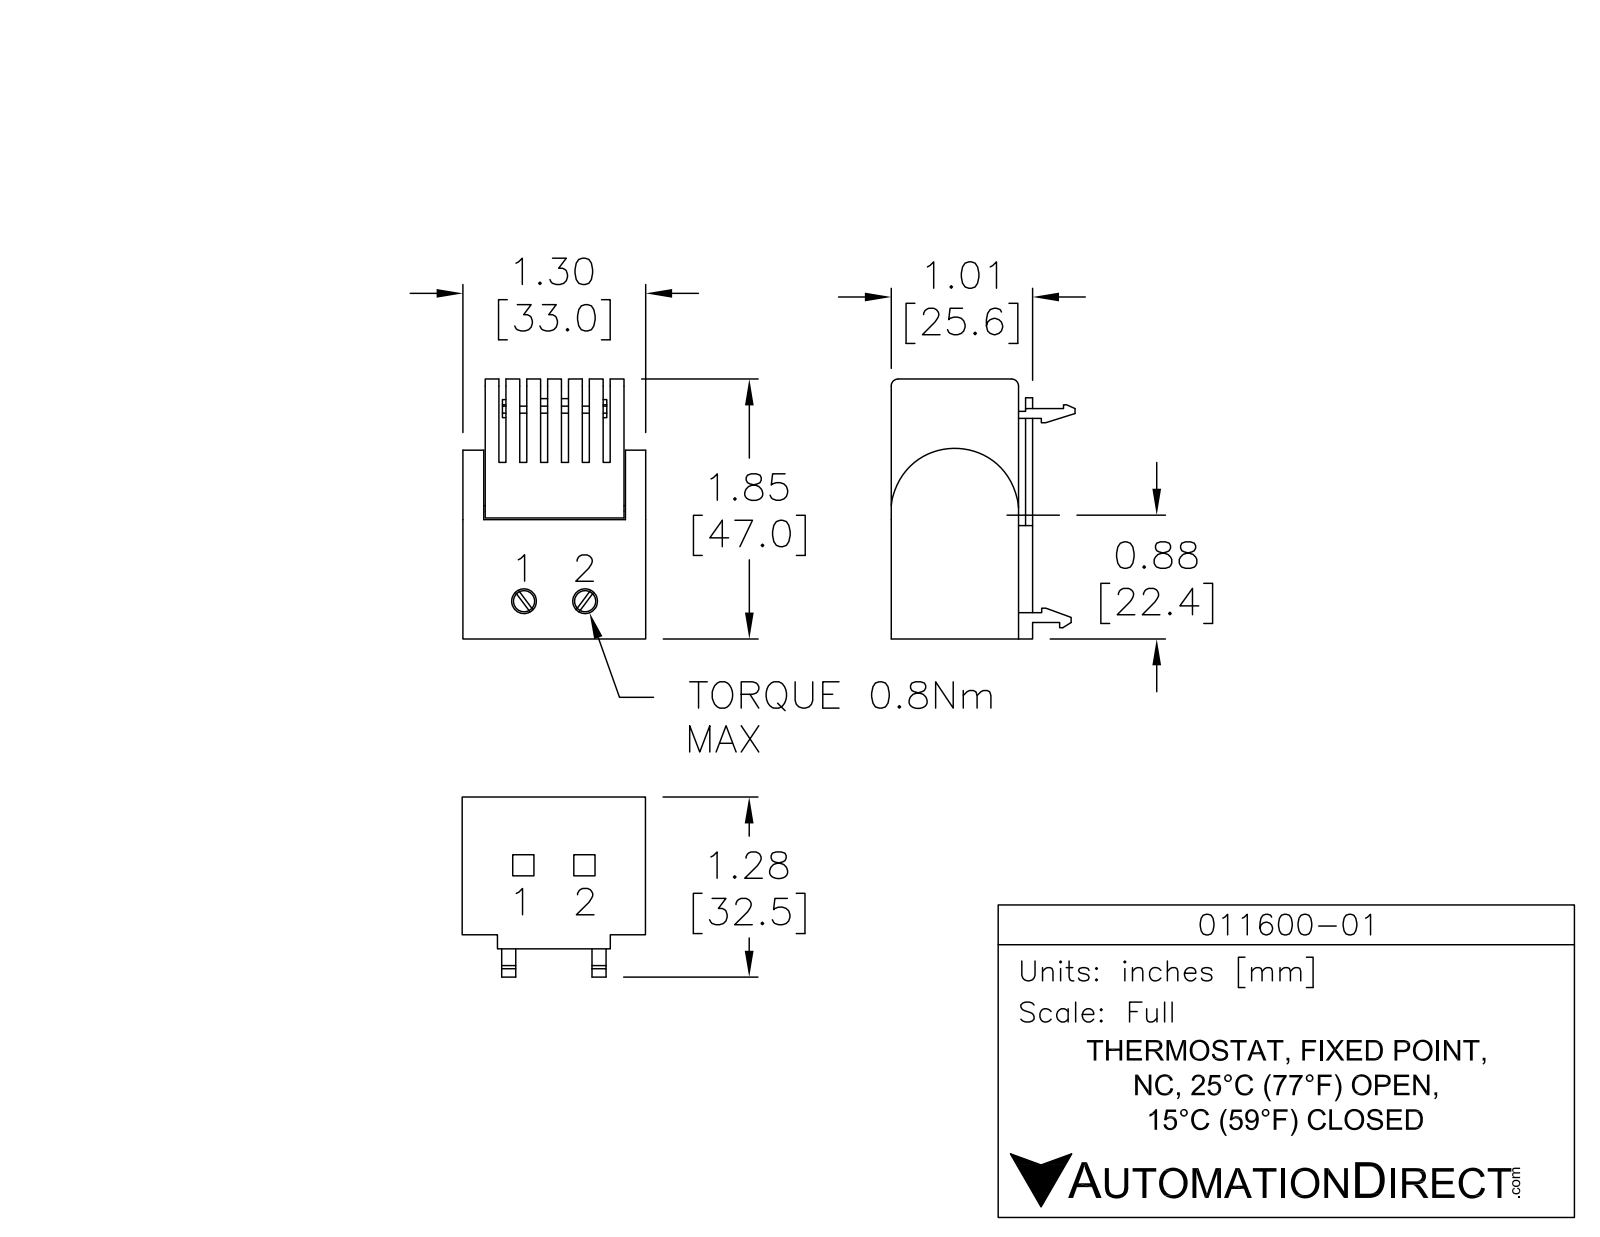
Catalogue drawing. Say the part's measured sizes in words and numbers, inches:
The part is named "011600-01". Its 3-D file was written by "SolidWorks 2013 (AUTOMOTIVE_DESIGN)". It is 1 solid with 374 faces: 188 planar, 123 cylindrical and 63 other. Overall it measures 1.821 by 1.305 by 1.285 inches. Its volume is 1.989 cubic inches and its surface area 15.56 square inches. Partial cylindrical surfaces (rounded edges, fillets, slot ends): 16 of radius 0.025, 10 of radius 0.023, 8 of radius 0.03, 7 of radius 0.015, 7 of radius 0.06, 4 of radius 0.04, 3 of radius 0.026, 2 of radius 0.026. The main face-to-face distances are 1.305, 0.095, 0.91, 0.911, 0.178, 1.127, 0.14, 0.28, 0.028, 1.821.
